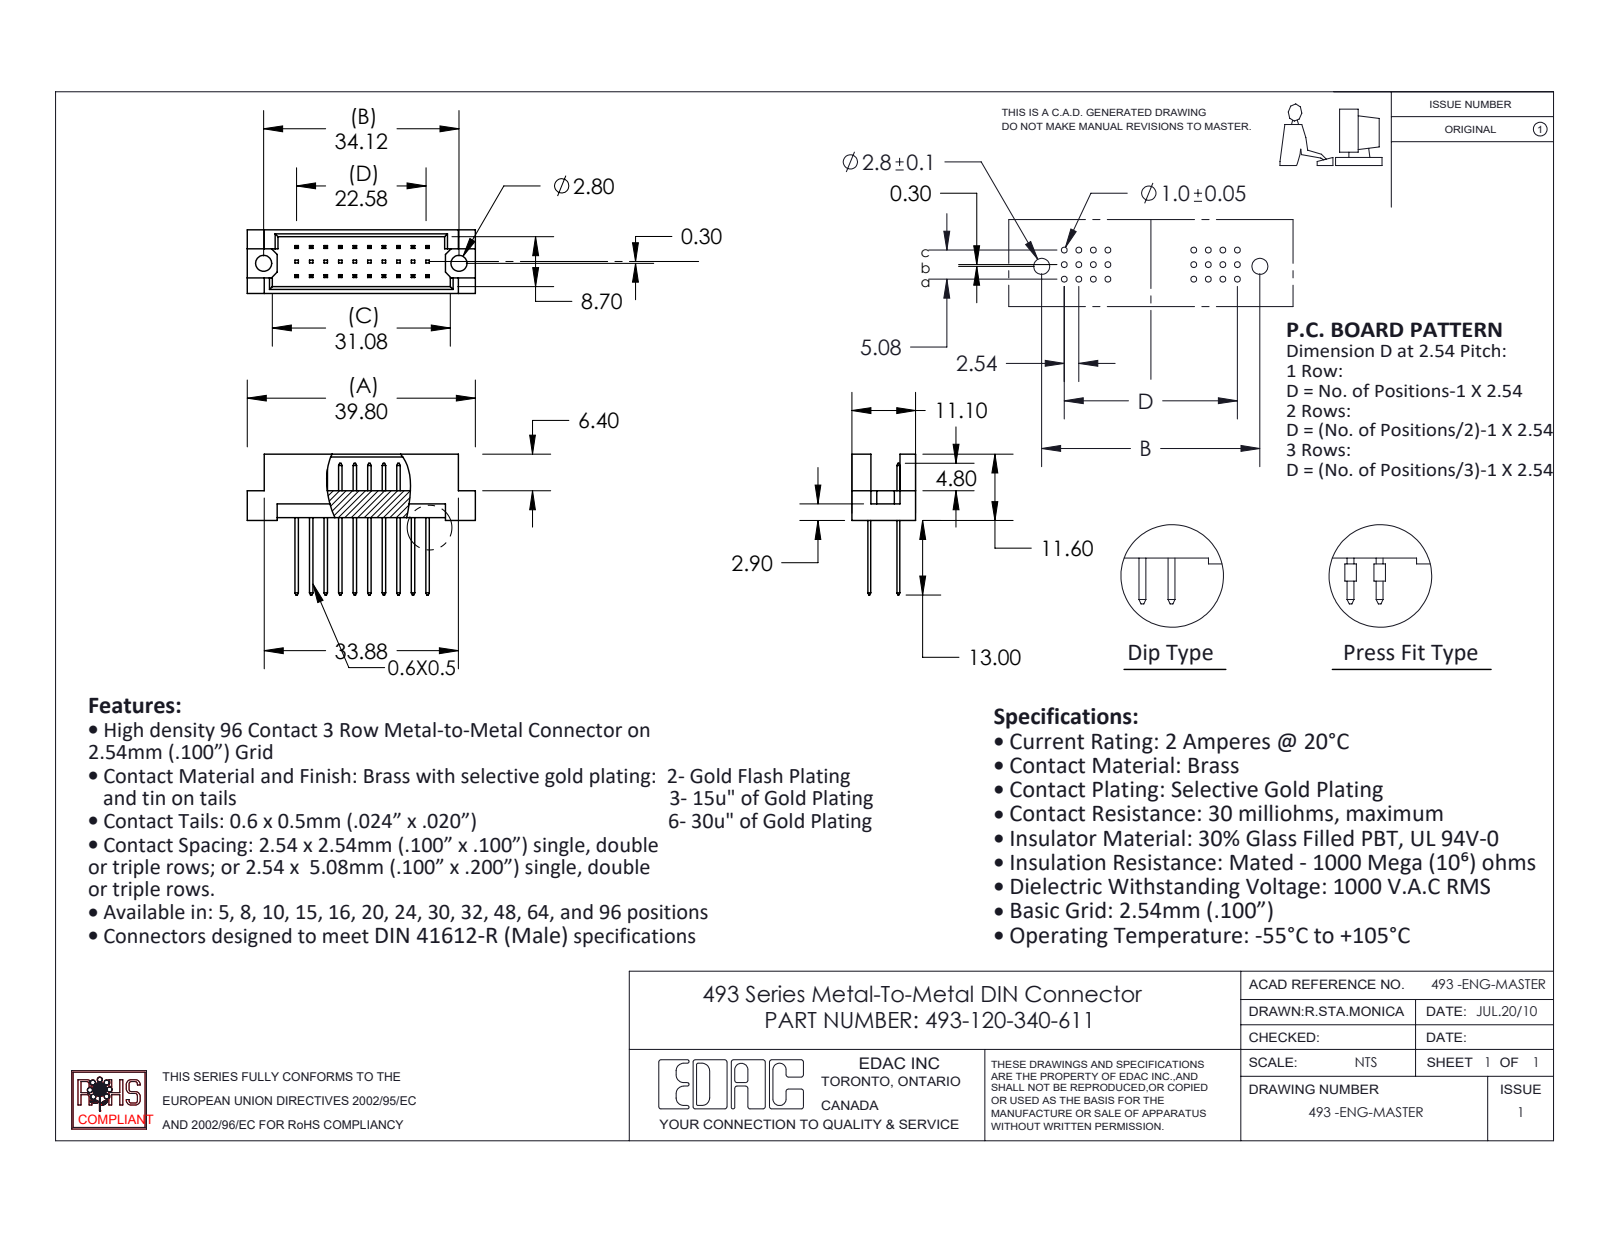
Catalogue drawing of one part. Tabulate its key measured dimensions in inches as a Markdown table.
| quantity | value |
| --- | --- |
| part name | 493 Part_30; 493-120-340-611; 493-290_40 |
| STEP written by | SolidWorks 2020 (CONFIG_CONTROL_DESIGN) |
| units | inches |
| bodies | 21 solids, 452 faces (448 planar, 4 cylindrical, 0 other) |
| overall size | 1.567 × 0.969 × 0.437 |
| volume | 0.153 in³ |
| surface area | 5.8 in² |
| round holes (diameter × count) | 0.11 × 2 |
| main face-to-face distances | 0.2, 0.1, 0.047, 0.39, 0.02, 0.437, 0.109, 0.128, 0.309, 0.328 |
| hole center spacings | 1.343 |
